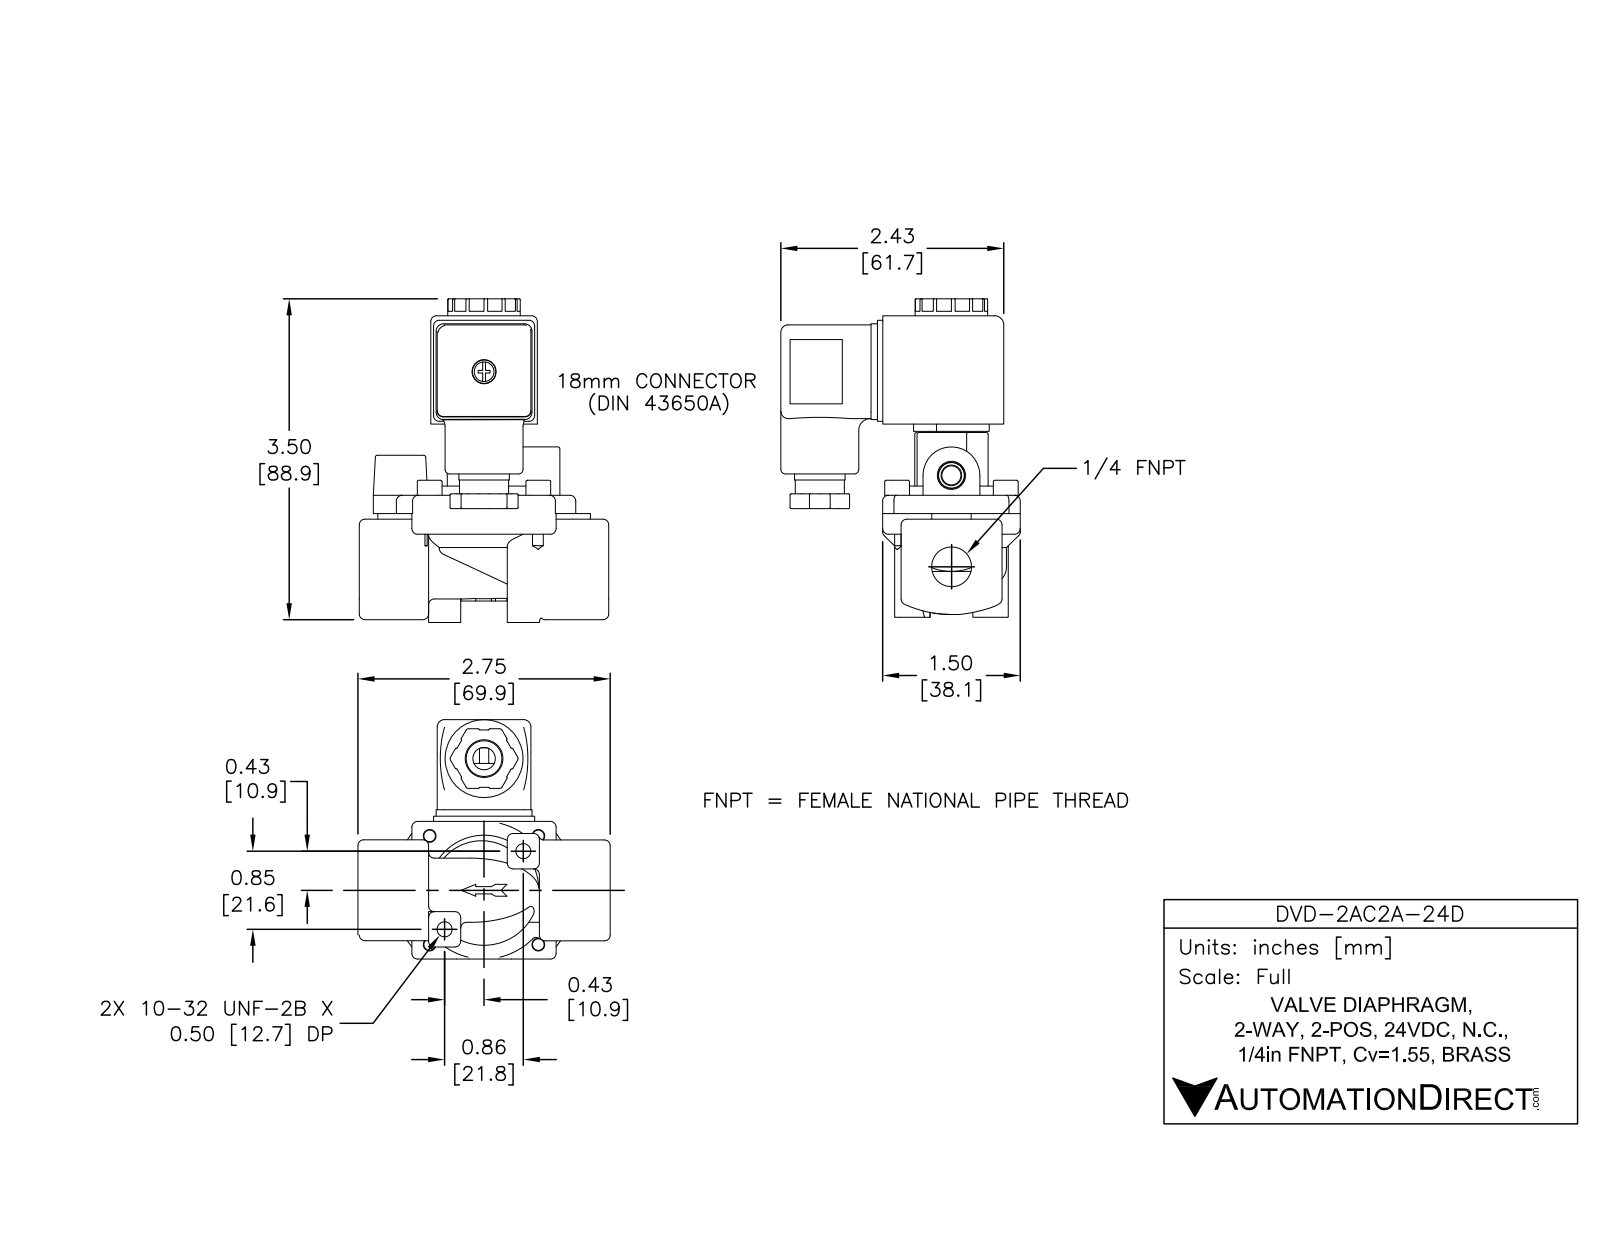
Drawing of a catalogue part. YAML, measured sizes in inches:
part_name: "DVD-2AC2A-24D"
step_written_by: "SolidWorks 2015 (AUTOMOTIVE_DESIGN)"
units: inches
bodies: {solids: 1, faces: 1779, planar: 848, cylindrical: 363, other: 568}
overall_size: [3.472, 2.72, 2.61]
volume: 5.884
surface_area: 63.91
round_holes:
  - {diameter: 0.139, count: 4}
  - {diameter: 0.06, count: 2}
  - {diameter: 0.098, count: 2}
  - {diameter: 0.14, count: 2}
  - {diameter: 0.164, count: 2}
  - {diameter: 0.434, count: 2}
  - {diameter: 0.062, count: 1}
  - {diameter: 0.077, count: 1}
  - {diameter: 0.089, count: 1}
  - {diameter: 0.093, count: 1}
  - {diameter: 0.102, count: 1}
  - {diameter: 0.12, count: 1}
round_bosses_or_shafts:
  - {diameter: 0.27, count: 4}
  - {diameter: 0.16, count: 4}
  - {diameter: 1.375, count: 1}
  - {diameter: 0.85, count: 1}
  - {diameter: 0.79, count: 1}
  - {diameter: 0.609, count: 1}
  - {diameter: 0.535, count: 1}
  - {diameter: 0.405, count: 1}
partial_cylinders:
  - {radius: 0.01, count: 52}
  - {radius: 0.063, count: 29}
  - {radius: 0.062, count: 21}
  - {radius: 0.08, count: 12}
  - {radius: 0.156, count: 12}
  - {radius: 0.05, count: 8}
  - {radius: 0.062, count: 7}
  - {radius: 0.03, count: 6}
face_to_face_distances: [0.925, 1.161, 0.2, 0.08, 1.036, 1.1, 1.181, 0.956, 1.3, 0.06]
hole_center_spacings: [0.924, 0.838, 1.185, 0.233, 0.389, 0.449, 0.605, 0.672]
